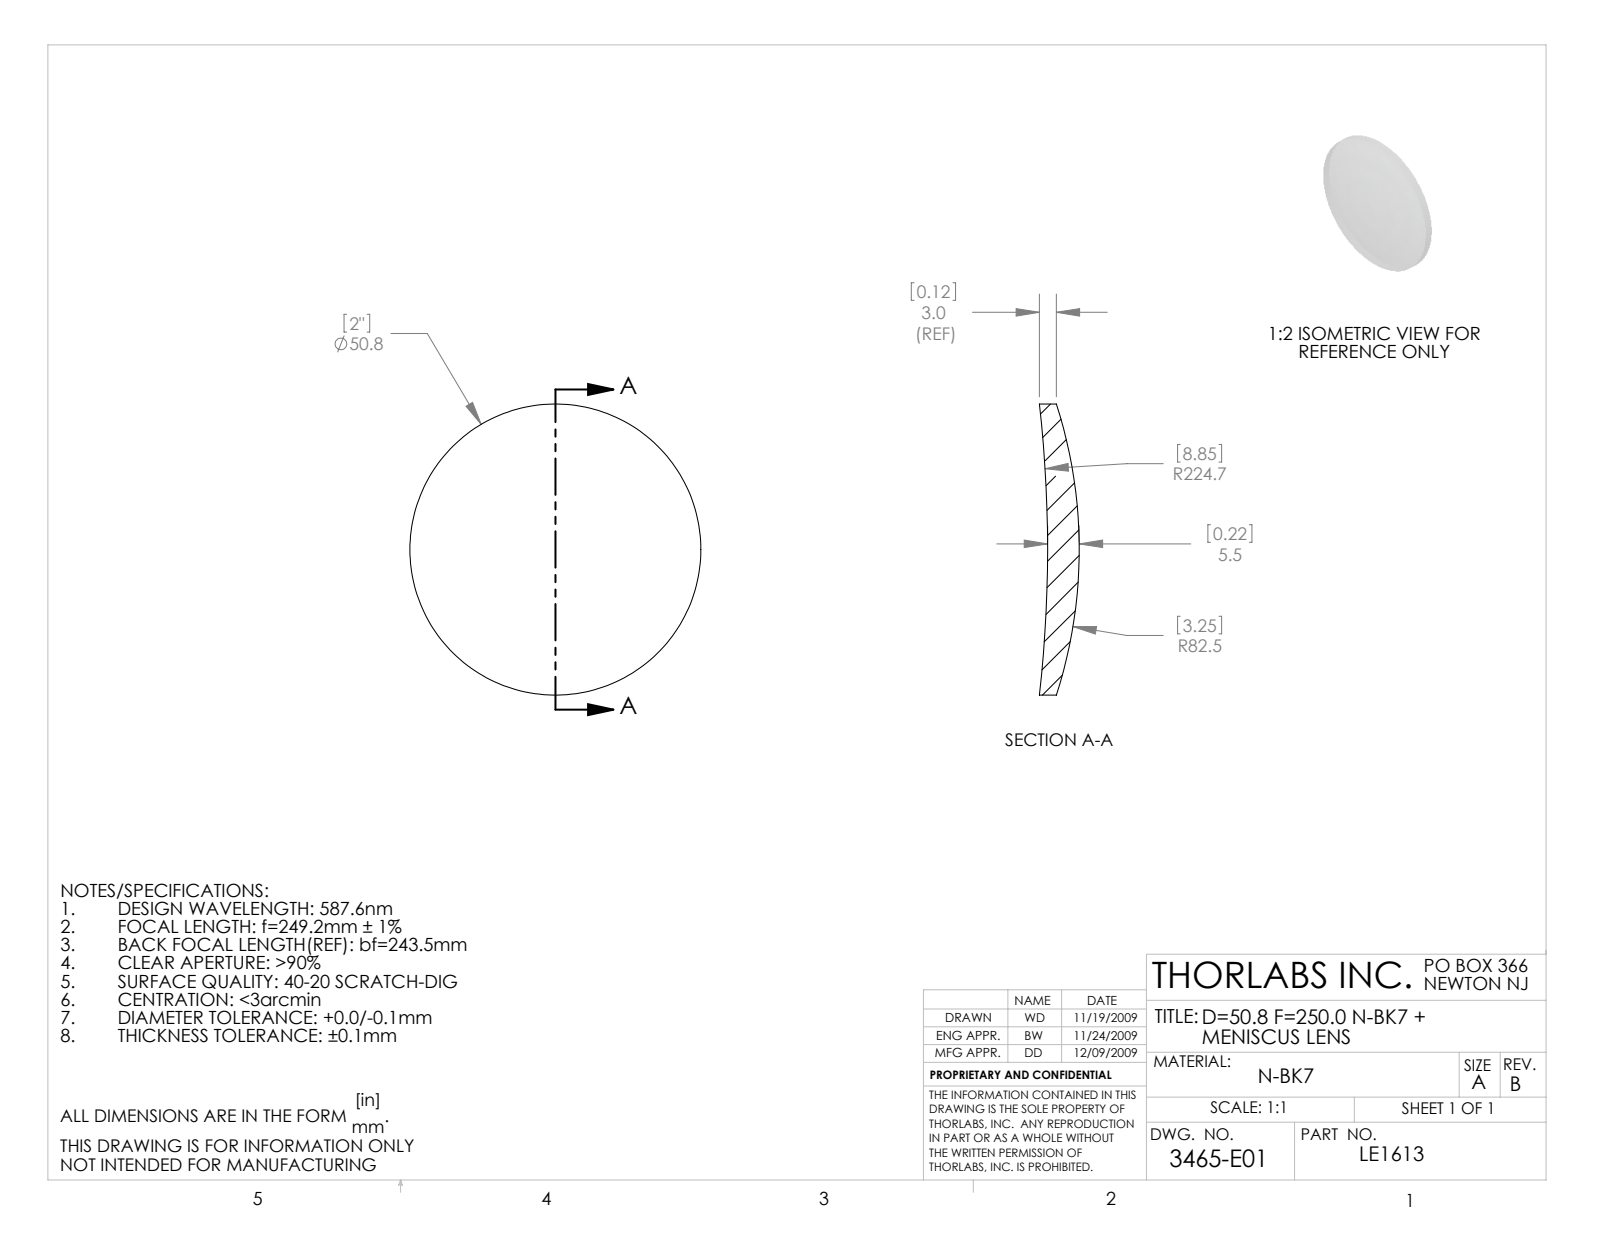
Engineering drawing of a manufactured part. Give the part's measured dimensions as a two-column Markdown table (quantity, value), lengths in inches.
| quantity | value |
| --- | --- |
| part name | 3465-E0W |
| STEP written by | SolidWorks 2009 (AUTOMOTIVE_DESIGN) |
| units | inches |
| bodies | 1 solid, 6 faces (0 planar, 2 cylindrical, 4 other) |
| overall size | 2 × 2 × 0.274 |
| volume | 0.527 in³ |
| surface area | 7.105 in² |
| round bosses / shafts (diameter × count) | 2 × 1 |
